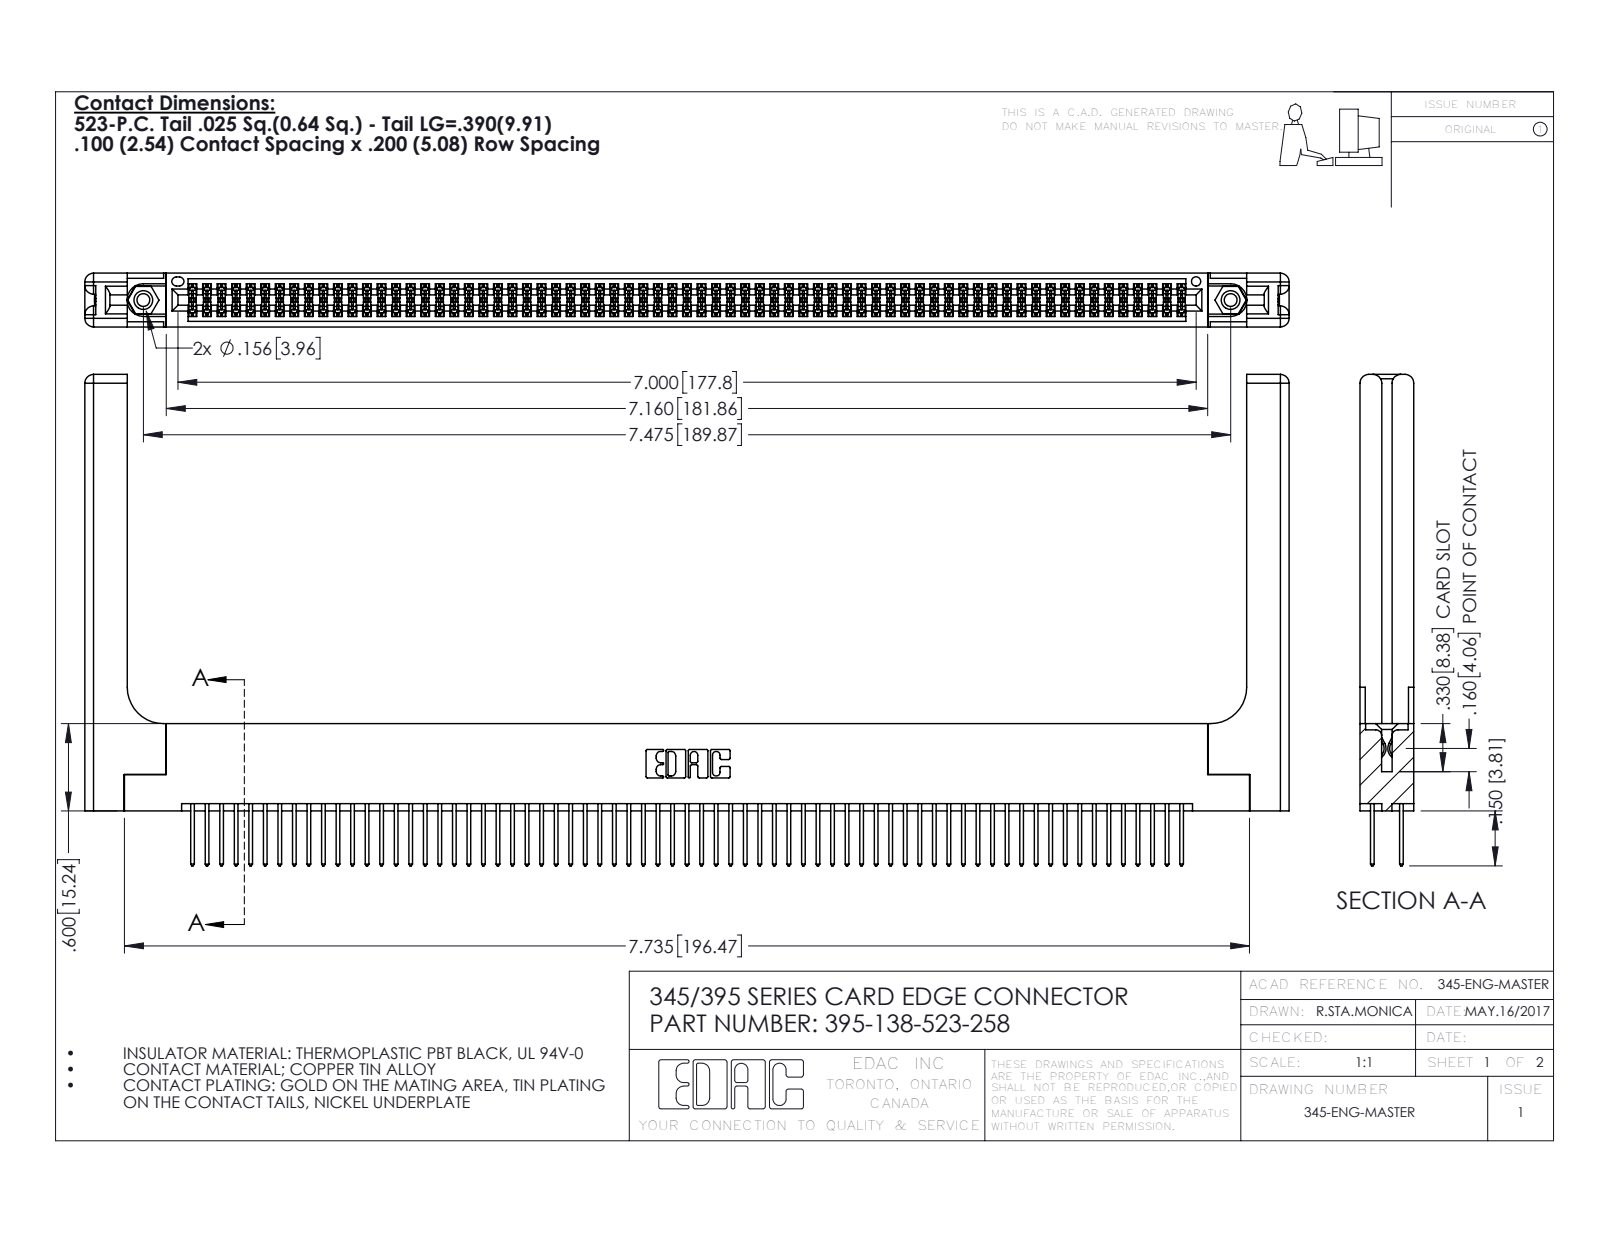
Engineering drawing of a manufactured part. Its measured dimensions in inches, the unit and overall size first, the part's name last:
Units: inches
Overall size (bounding box): 8.279 × 3.377 × 0.37
Round holes (diameter × count): ⌀0.089 ×2, ⌀0.125 ×2, ⌀0.156 ×2, ⌀0.064 ×1
Round bosses / shafts (diameter × count): ⌀0.155 ×2
Partial cylindrical surfaces — rounded edges, fillets, slot ends (radius × count): R0.006 ×207, R0.01 ×138, R0.01 ×22, R0.06 ×16, R0.007 ×6, R0.031 ×6, R0.026 ×3, R0.014 ×2
Main face-to-face distances: 0.072, 0.298, 0.37, 0.2, 0.098, 0.272, 0.025, 0.225, 0.175, 0.148
Hole centre spacings: 0.27, 7.239, 7.475
Volume: 1.796 in³ · Surface area: 58.64 in²
Bodies: 143 solids, 7282 faces (4782 planar, 2440 cylindrical, 60 other)
Part name (STEP PRODUCT): 345-220-058_345-220-058; 345-292-001_345-293-123; 345 Part_Flush Mounting Lugs - 0.156 Dia-TH; 395-138-523-258 (+1 more)
STEP written by: SolidWorks 2016 (CONFIG_CONTROL_DESIGN)
